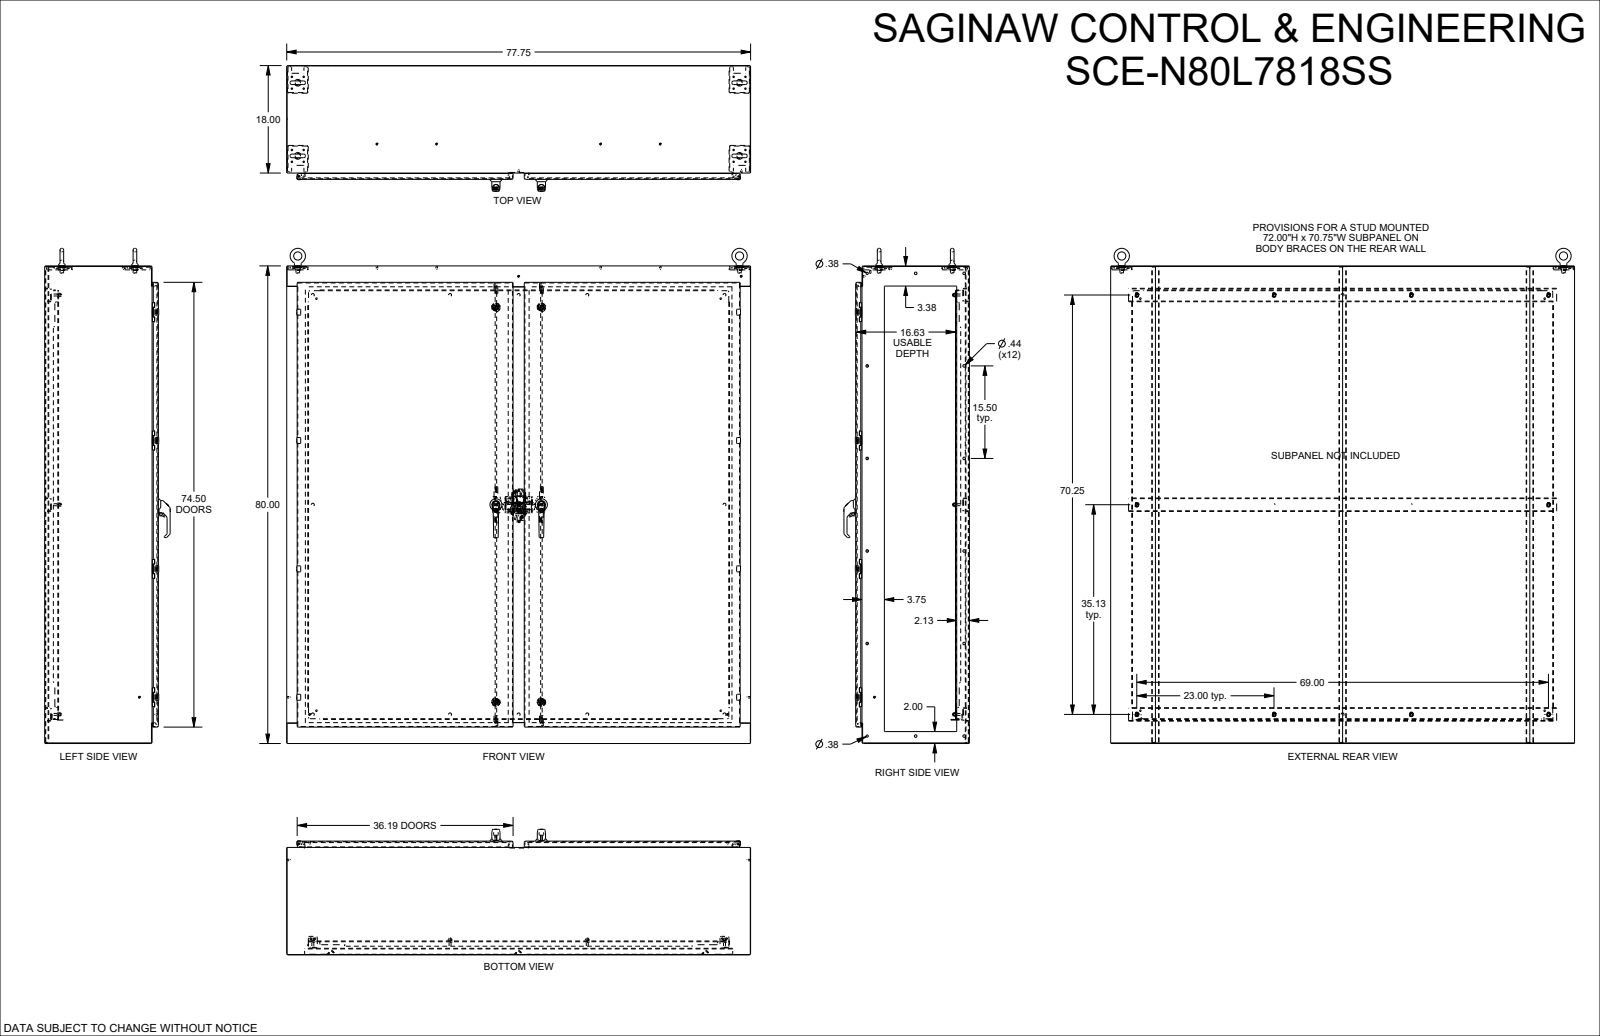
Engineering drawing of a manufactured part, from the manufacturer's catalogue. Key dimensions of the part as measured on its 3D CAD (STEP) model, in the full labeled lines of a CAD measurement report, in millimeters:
Part name (STEP PRODUCT): SCE-N80L7818
STEP written by: SolidWorks 2023 (AUTOMOTIVE_DESIGN)
Units: millimetres
Bodies: 48 solids, 7358 faces (3020 planar, 2474 cylindrical, 1864 other)
Overall size (bounding box): 2106.8 × 1974.9 × 534.6
Volume: 34 590 000 mm³ · Surface area: 25 860 000 mm²
Round holes (diameter × count): ⌀6.4 ×20, ⌀9.5 ×18, ⌀5.2 ×16, ⌀6.2 ×16, ⌀11.1 ×12, ⌀1 ×8, ⌀4.3 ×8, ⌀5.5 ×8, ⌀6.5 ×4, ⌀8.7 ×4, ⌀8.7 ×4, ⌀9.1 ×4
Round bosses / shafts (diameter × count): ⌀4.3 ×24, ⌀6.4 ×20, ⌀6.1 ×16, ⌀5 ×10, ⌀35.6 ×4, ⌀29.8 ×4, ⌀15.2 ×4, ⌀8.7 ×4
Partial cylindrical surfaces — rounded edges, fillets, slot ends (radius × count): R0.8 ×196, R0.4 ×166, R3.2 ×100, R0.5 ×72, R0.5 ×48, R1 ×42, R1 ×40, R4.2 ×38
Main face-to-face distances: 2.6, 481.4, 484.1, 478.8, 2029.4, 454.6, 26.9, 451.9, 29.5, 2032
Hole centre spacings: 50.3, 393.7, 570.4, 1092.2, 35.6, 546.1, 787.4, 889
